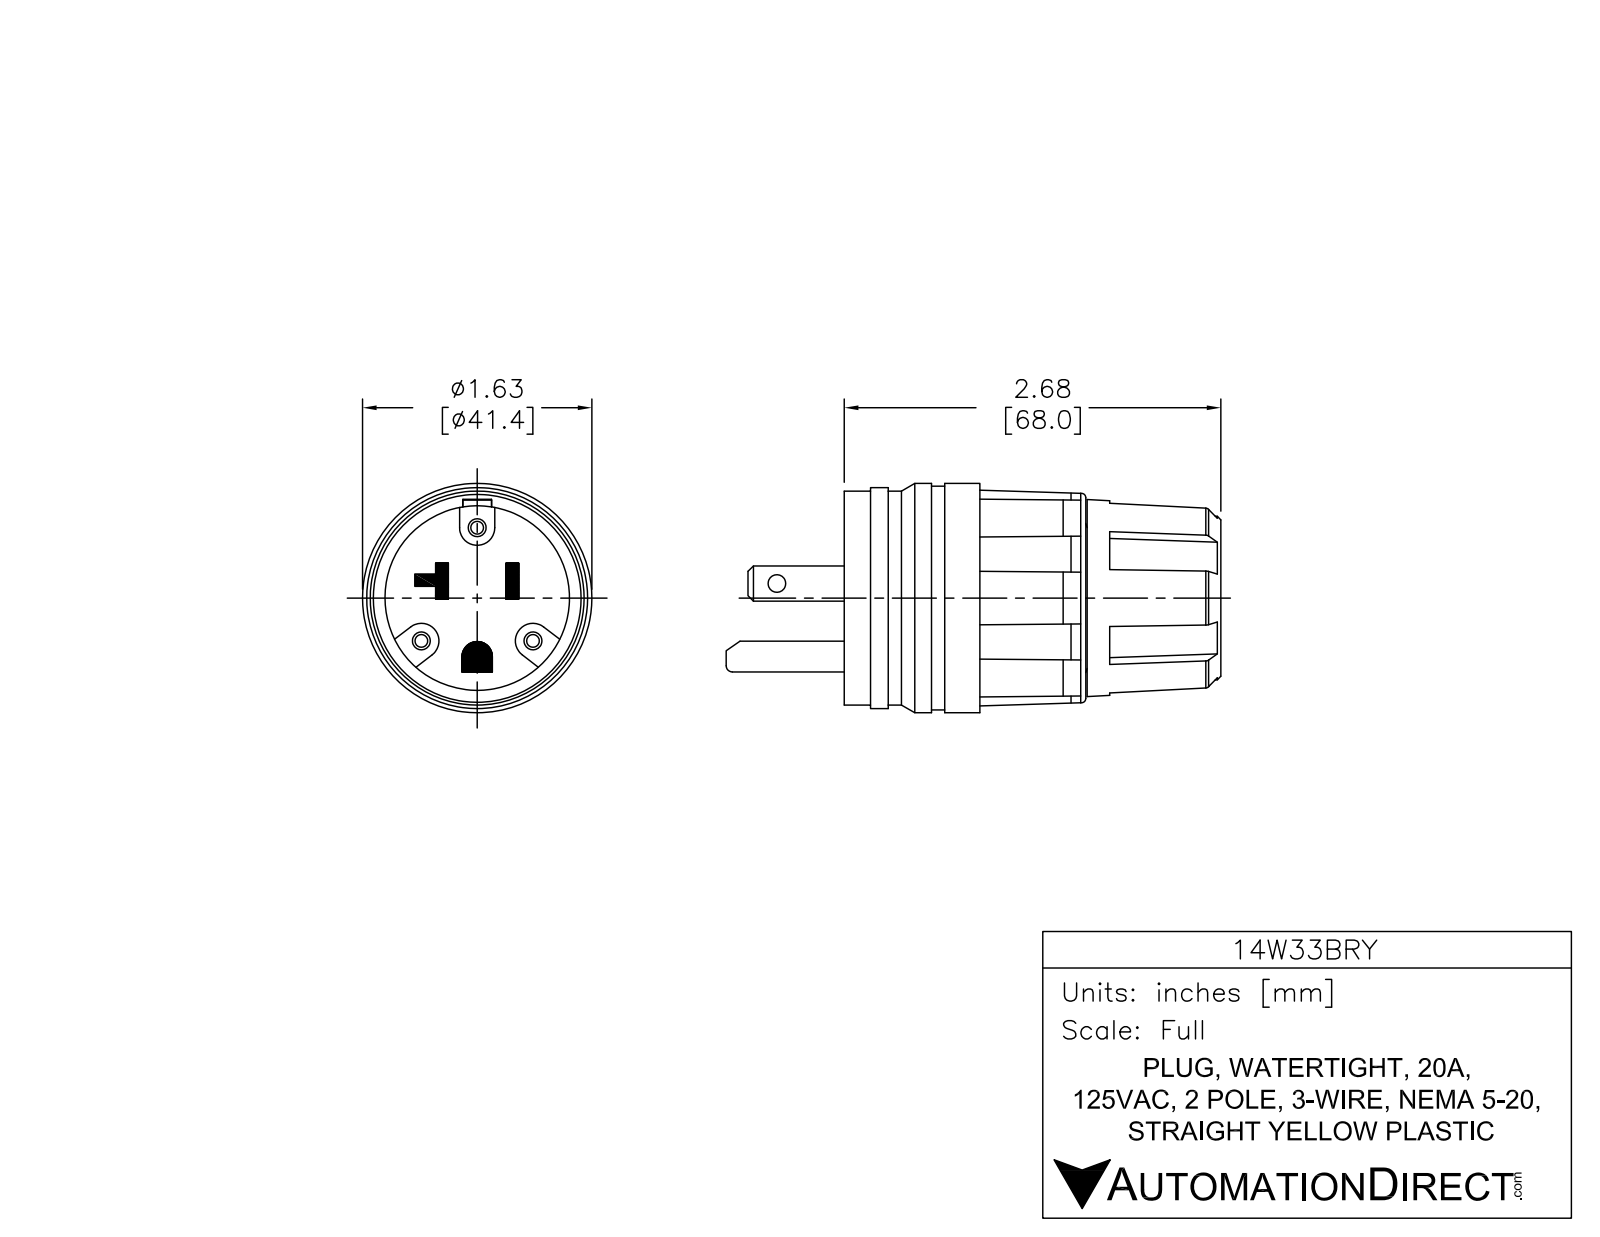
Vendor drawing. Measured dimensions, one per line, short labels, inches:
name: 14W33BRY
written by: SolidWorks 2013 (AUTOMOTIVE_DESIGN)
unit: in
bodies: 1 solid, 206 faces (93 planar, 41 cylindrical, 72 other)
size: 3.587 × 1.615 × 1.615
volume: 4.173 in³; area: 23.08 in²
holes: 2× ⌀0.12, 1× ⌀0.625, 1× ⌀1.15, 1× ⌀1.3
bosses: 3× ⌀0.19, 1× ⌀1.615, 1× ⌀1.56, 1× ⌀1.51, 1× ⌀1
rounds: 3× R0.06, 3× R0.11, 2× R0.03, 1× R0.05
face distances: 1.822, 2.757, 0.935, 1.702, 0.12, 1.055, 0.013, 1.715, 1.835, 2.77
